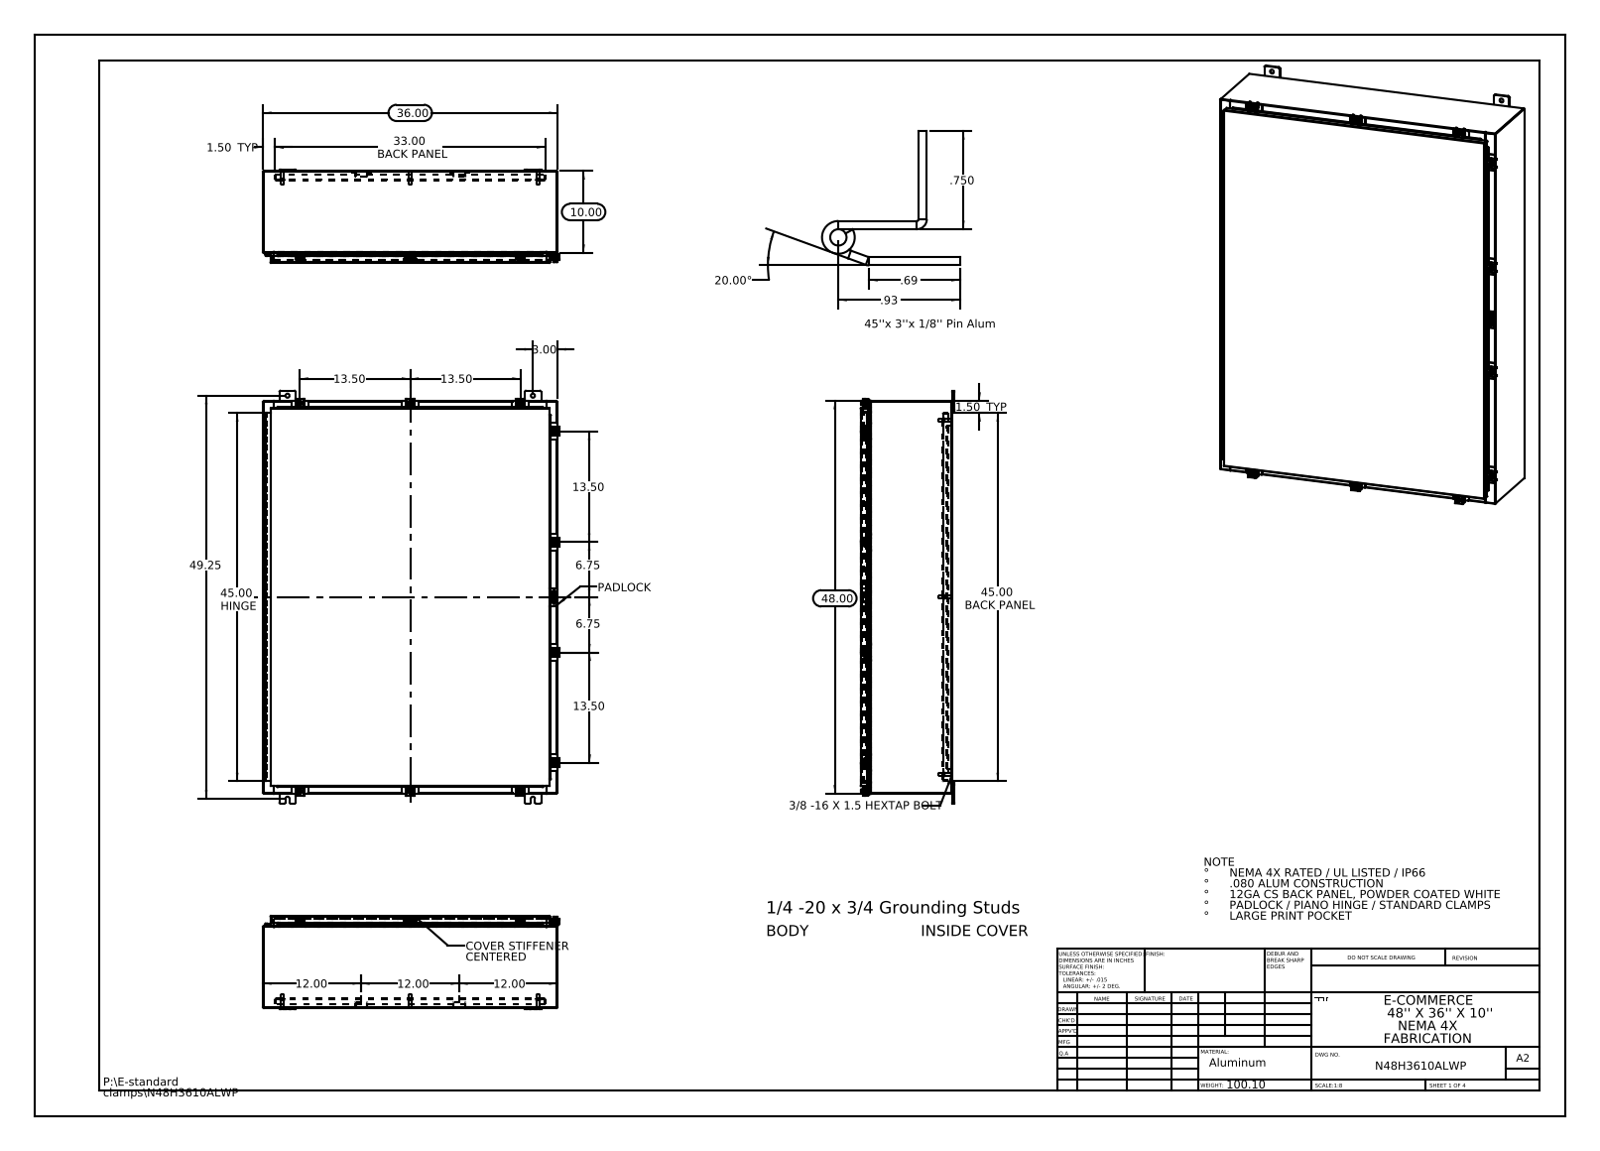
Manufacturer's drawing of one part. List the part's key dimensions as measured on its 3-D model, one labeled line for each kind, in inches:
Part name (STEP PRODUCT): N48H3610ALWP Standard Clamps; N48H3610ALWP Cover; N48H3610ALWP Clamp Assembly; N48H3610ALWP Hinge Cover Side (+8 more)
STEP written by: SolidWorks 2013 (CONFIG_CONTROL_DESIGN)
Units: inches
Bodies: 74 solids, 2999 faces (1562 planar, 1269 cylindrical, 168 other)
Overall size (bounding box): 50.5 × 36.211 × 11.389
Volume: 625.8 in³ · Surface area: 15 588 in²
Round holes (diameter × count): ⌀0.5 ×12, ⌀0.213 ×10, ⌀0.26 ×10, ⌀0.25 ×6, ⌀0.125 ×2, ⌀0.125 ×1
Round bosses / shafts (diameter × count): ⌀0.25 ×11, ⌀0.5 ×10, ⌀0.399 ×10, ⌀0.625 ×8, ⌀0.375 ×8, ⌀0.33 ×8
Partial cylindrical surfaces — rounded edges, fillets, slot ends (radius × count): R0.06 ×46, R0.013 ×39, R0.088 ×33, R0.19 ×24, R0.12 ×20, R0.141 ×20, R0.05 ×15, R0.08 ×14
Main face-to-face distances: 0.075, 11.126, 11.051, 0.104, 11.201, 1, 10.126, 1.075, 10.051, 1.179
Hole centre spacings: 13.5, 13.663, 20, 20.123, 21.625, 23.82, 27, 38.003
